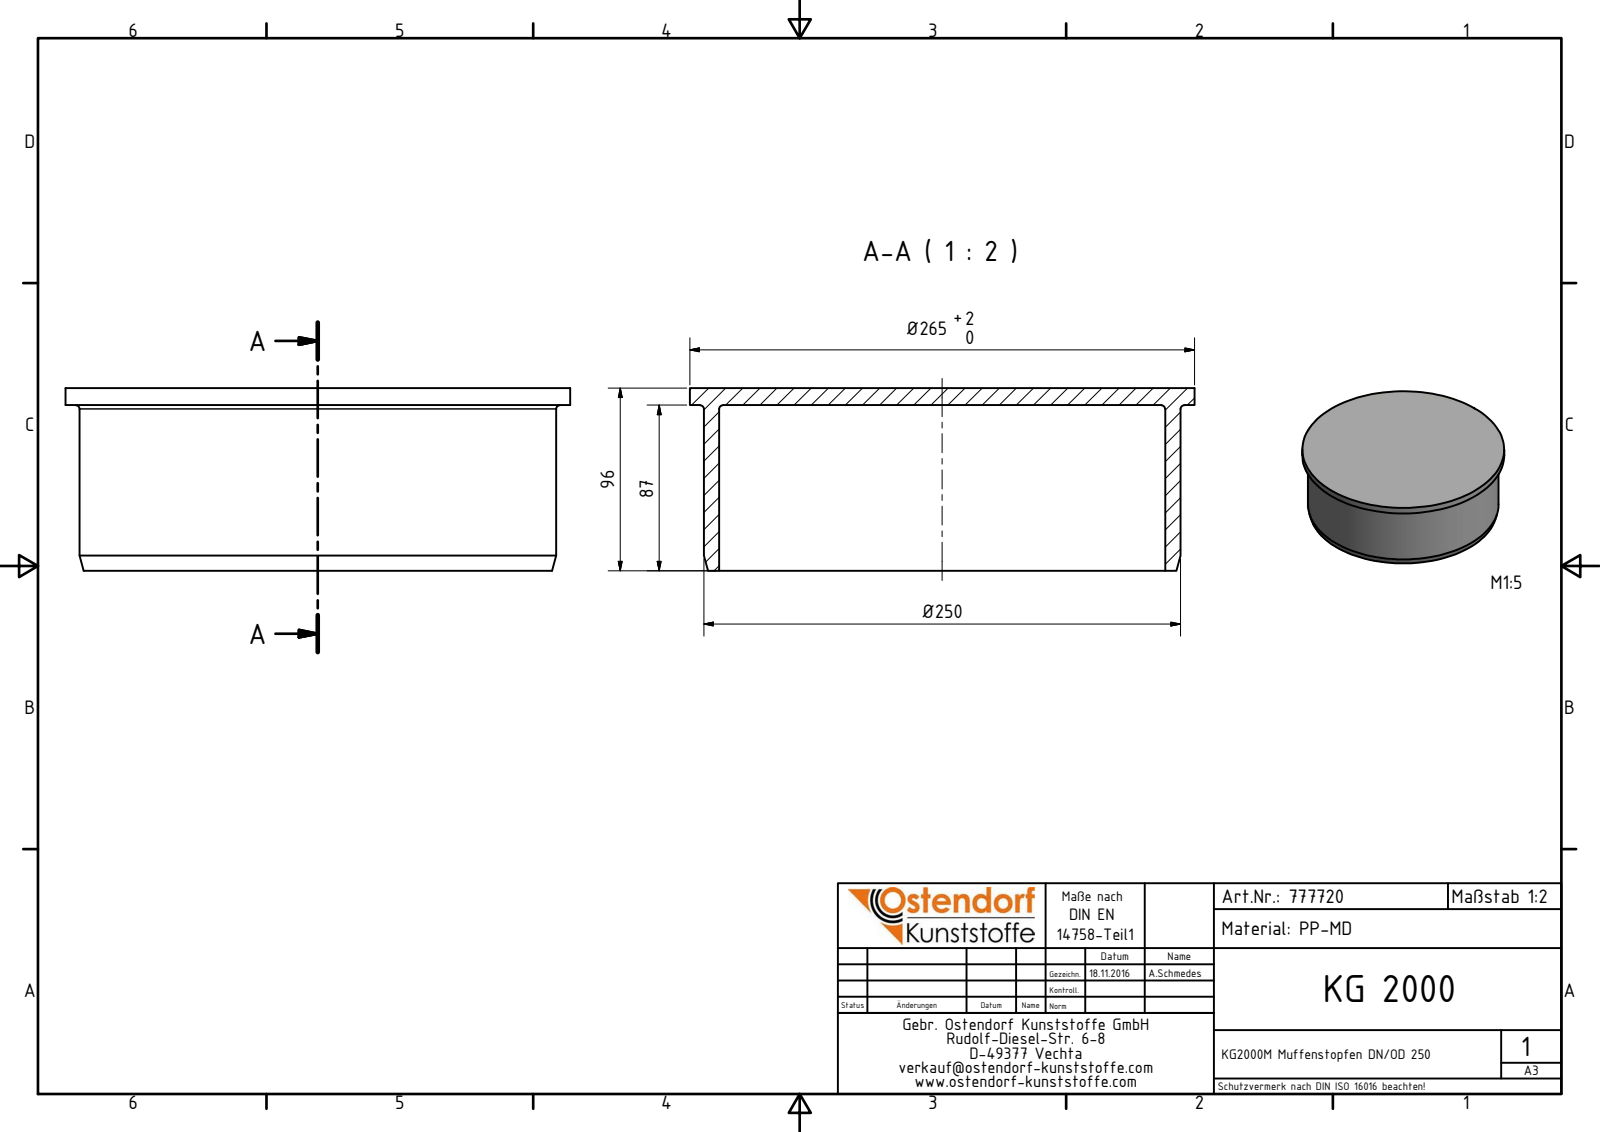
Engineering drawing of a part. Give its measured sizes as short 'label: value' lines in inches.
name: 777720 KG2000M Muffenstopfen DN_OD 250
written by: Autodesk Inventor 2016 (AUTOMOTIVE_DESIGN)
unit: in
bodies: 1 solid, 10 faces (4 planar, 3 cylindrical, 3 other)
size: 10.433 × 10.433 × 3.78
volume: 62.31 in³; area: 383.5 in²
holes: 1× ⌀9.224
bosses: 1× ⌀10.433, 1× ⌀9.854
face distances: 0.354, 3.425, 3.78
